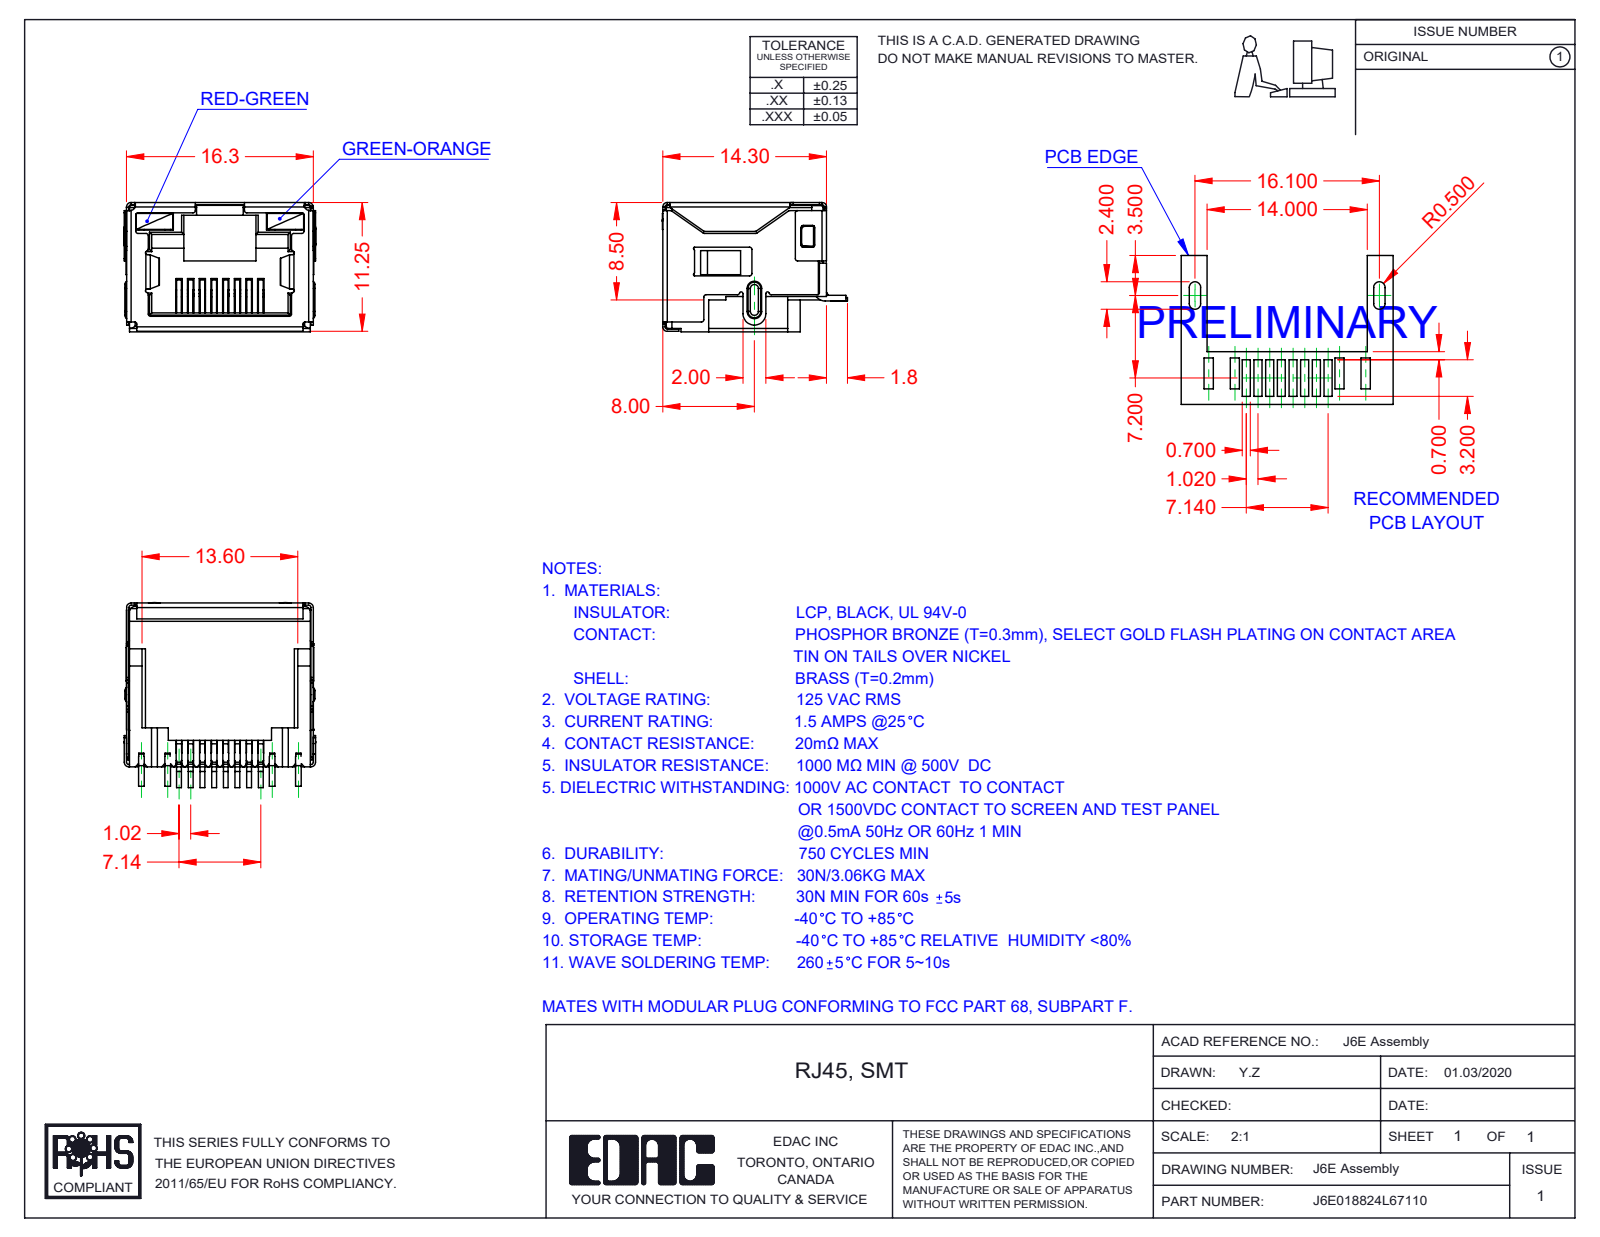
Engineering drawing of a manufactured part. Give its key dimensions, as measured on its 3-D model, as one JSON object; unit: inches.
{"part_name": "6E Contacts; 6E Insulator_LED; 6E Shield_LED; 6E LED RH_7-Green-Orange (+2 more)", "step_written_by": "SolidWorks 2016 (CONFIG_CONTROL_DESIGN)", "units": "inches", "bodies": {"solids": 12, "faces": 1500, "planar": 1099, "cylindrical": 351, "other": 50}, "overall_size": [0.659, 0.636, 0.445], "volume_in3": 0.068, "surface_area_in2": 6.27, "partial_cylinders_radius": [[0.008, 82], [0.01, 17], [0.016, 13], [0.02, 13], [0.004, 10], [0.006, 7], [0.012, 4], [0.039, 3]], "face_to_face_distances": [0.435, 0.632, 0.634, 0.624, 0.437, 0.445, 0.094, 0.028, 0.388, 0.019]}
